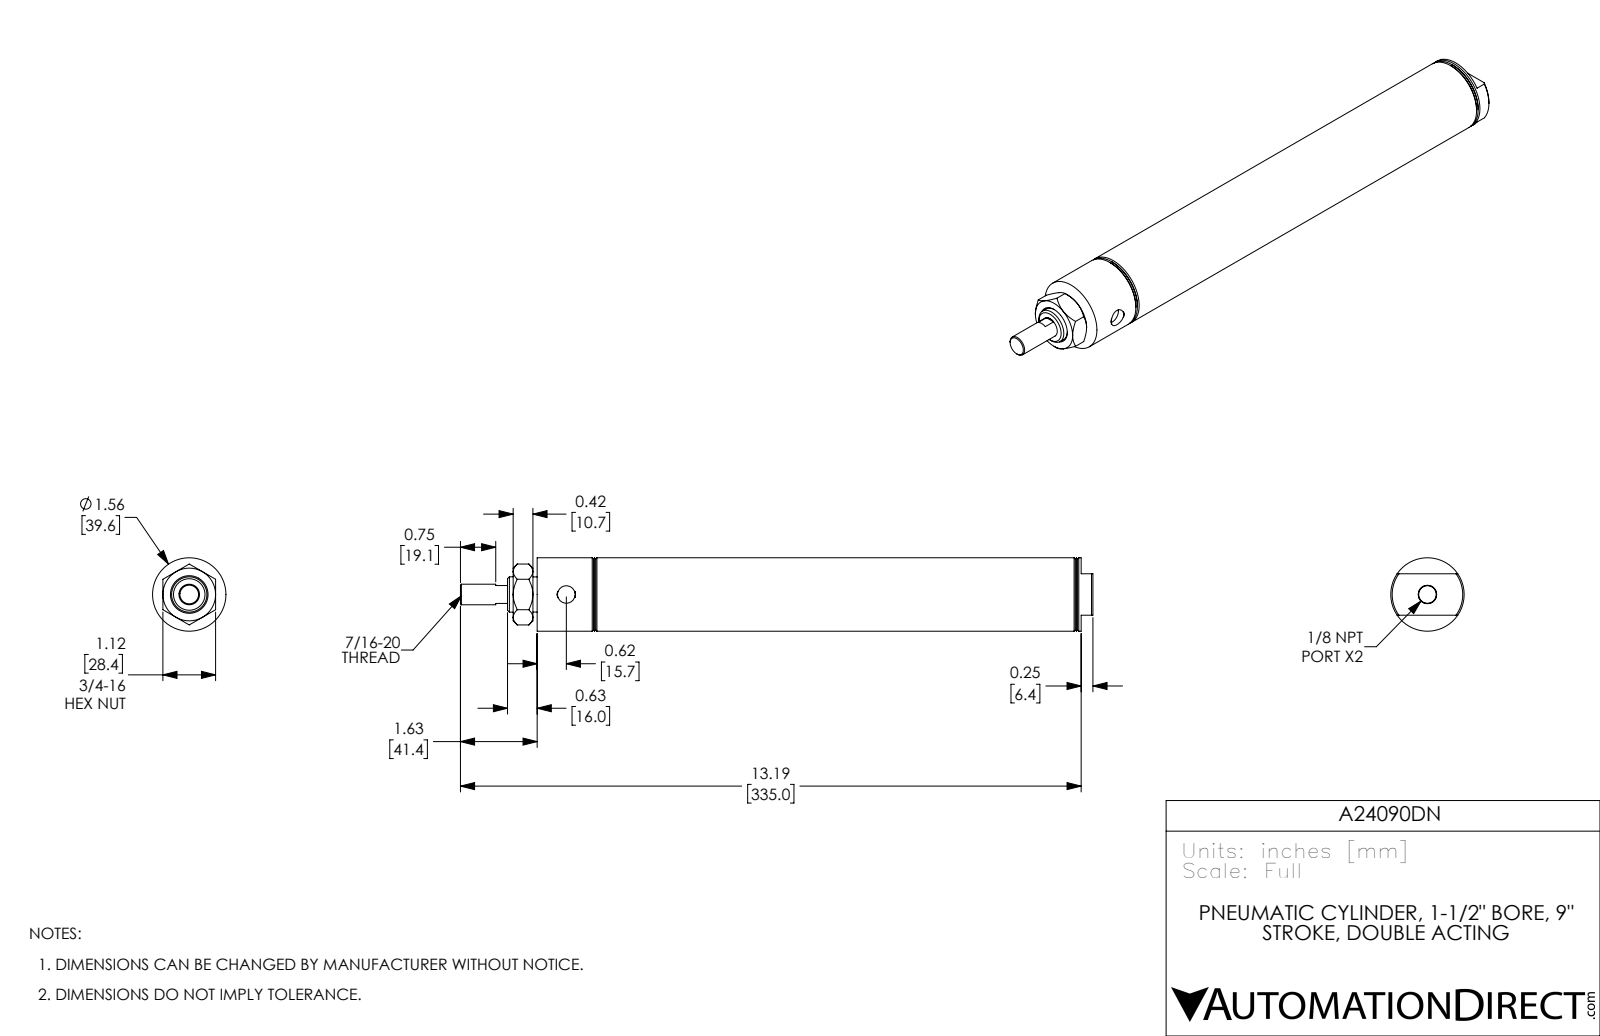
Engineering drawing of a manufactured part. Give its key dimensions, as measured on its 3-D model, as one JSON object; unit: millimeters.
{"part_name": "A24090DN; A24090DN_Mounting Nut_D-3556; A24090DN-Rod; A24090DN-MainBody", "step_written_by": "SolidWorks 2017 (AUTOMOTIVE_DESIGN)", "units": "millimeters", "bodies": {"solids": 3, "faces": 104, "planar": 32, "cylindrical": 24, "other": 48}, "overall_size": [341.4, 39.6, 39.6], "volume_mm3": 139200, "surface_area_mm2": 90640, "round_holes": [[9.5, 2], [11.1, 1], [19.1, 1], [38.1, 1]], "round_bosses_or_shafts": [[39.6, 1], [18.9, 1]], "face_to_face_distances": [241.3, 12.7, 228.6, 275.3, 262.6, 34, 24.6, 37.3, 265.9, 300]}
